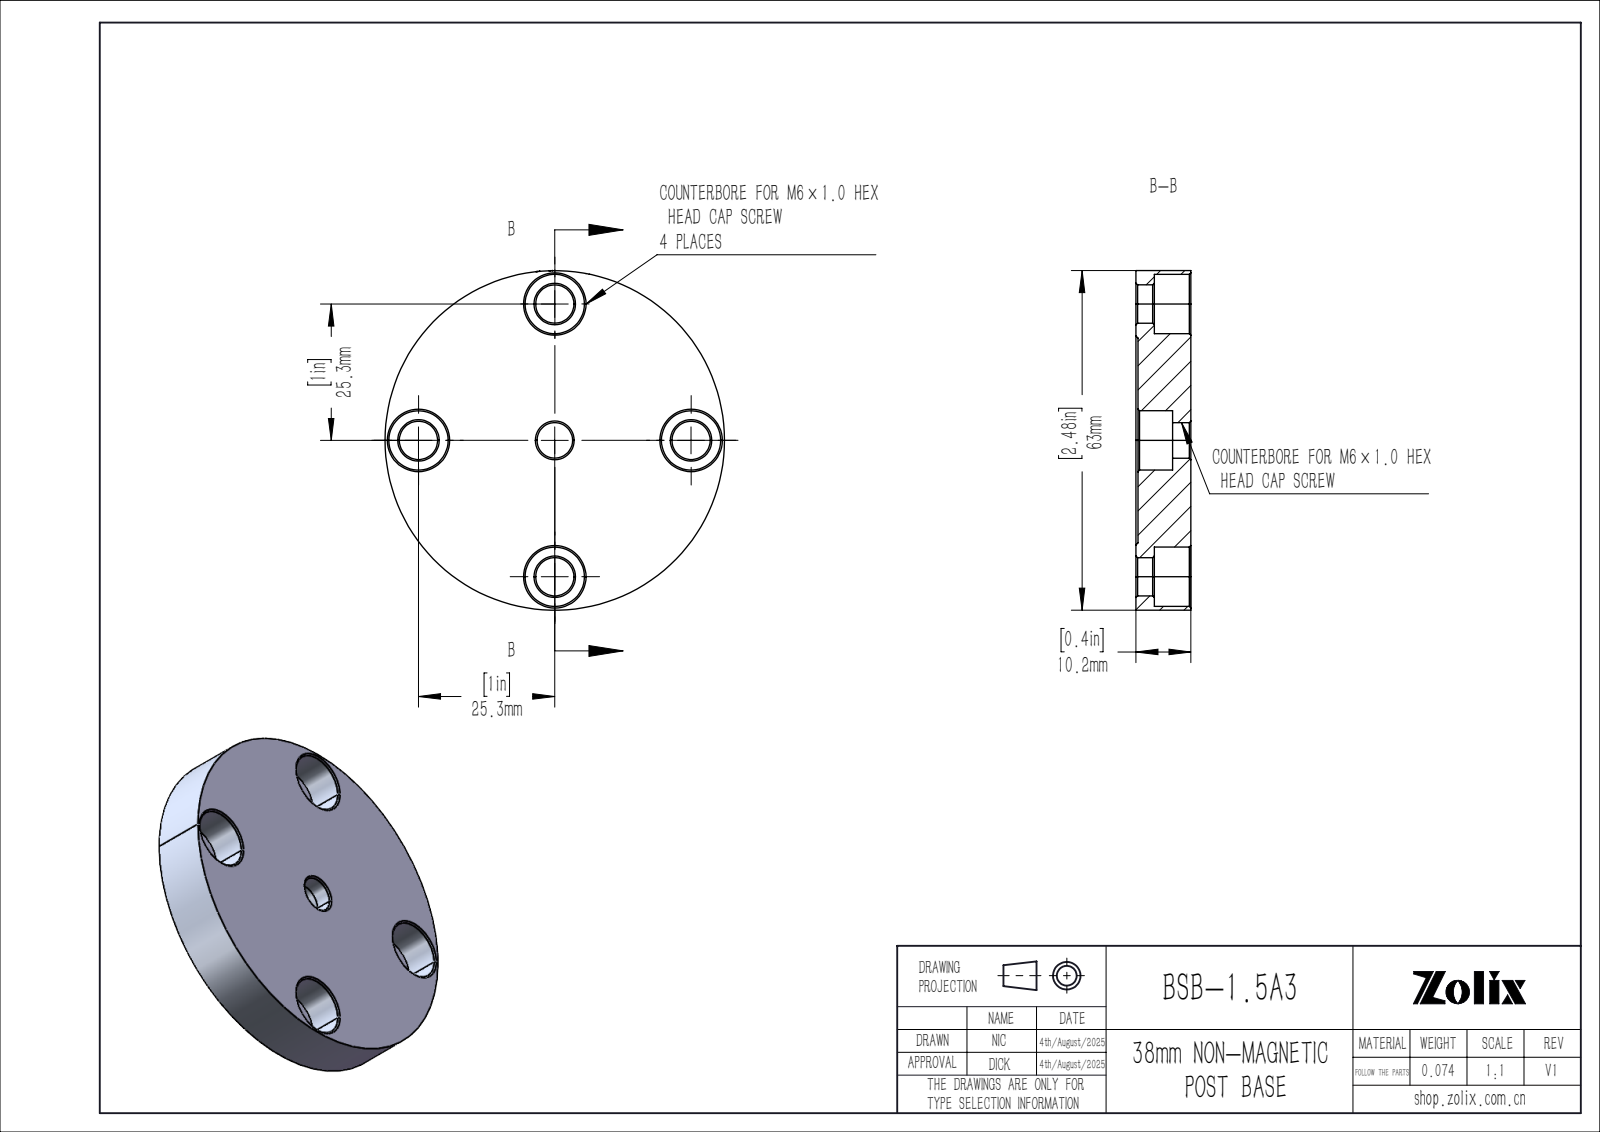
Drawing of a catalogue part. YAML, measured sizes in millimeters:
part_name: "BSB-1.5A3"
step_written_by: "SolidWorks 2020 (CONFIG_CONTROL_DESIGN)"
units: millimeters
bodies: {solids: 1, faces: 365, planar: 15, cylindrical: 46, other: 304}
overall_size: [63, 63, 10.2]
volume: 27492
surface_area: 9362
round_holes:
  - {diameter: 11, count: 5}
  - {diameter: 7.1, count: 4}
  - {diameter: 6.6, count: 1}
round_bosses_or_shafts:
  - {diameter: 63, count: 1}
partial_cylinders:
  - {radius: 31.48, count: 1}
face_to_face_distances: [10.2, 0.38, 9.82, 3.4, 6.8, 3.02, 6.42, 5.5, 5.12, 2.1]
hole_center_spacings: [25.3, 35.78, 50.6]
